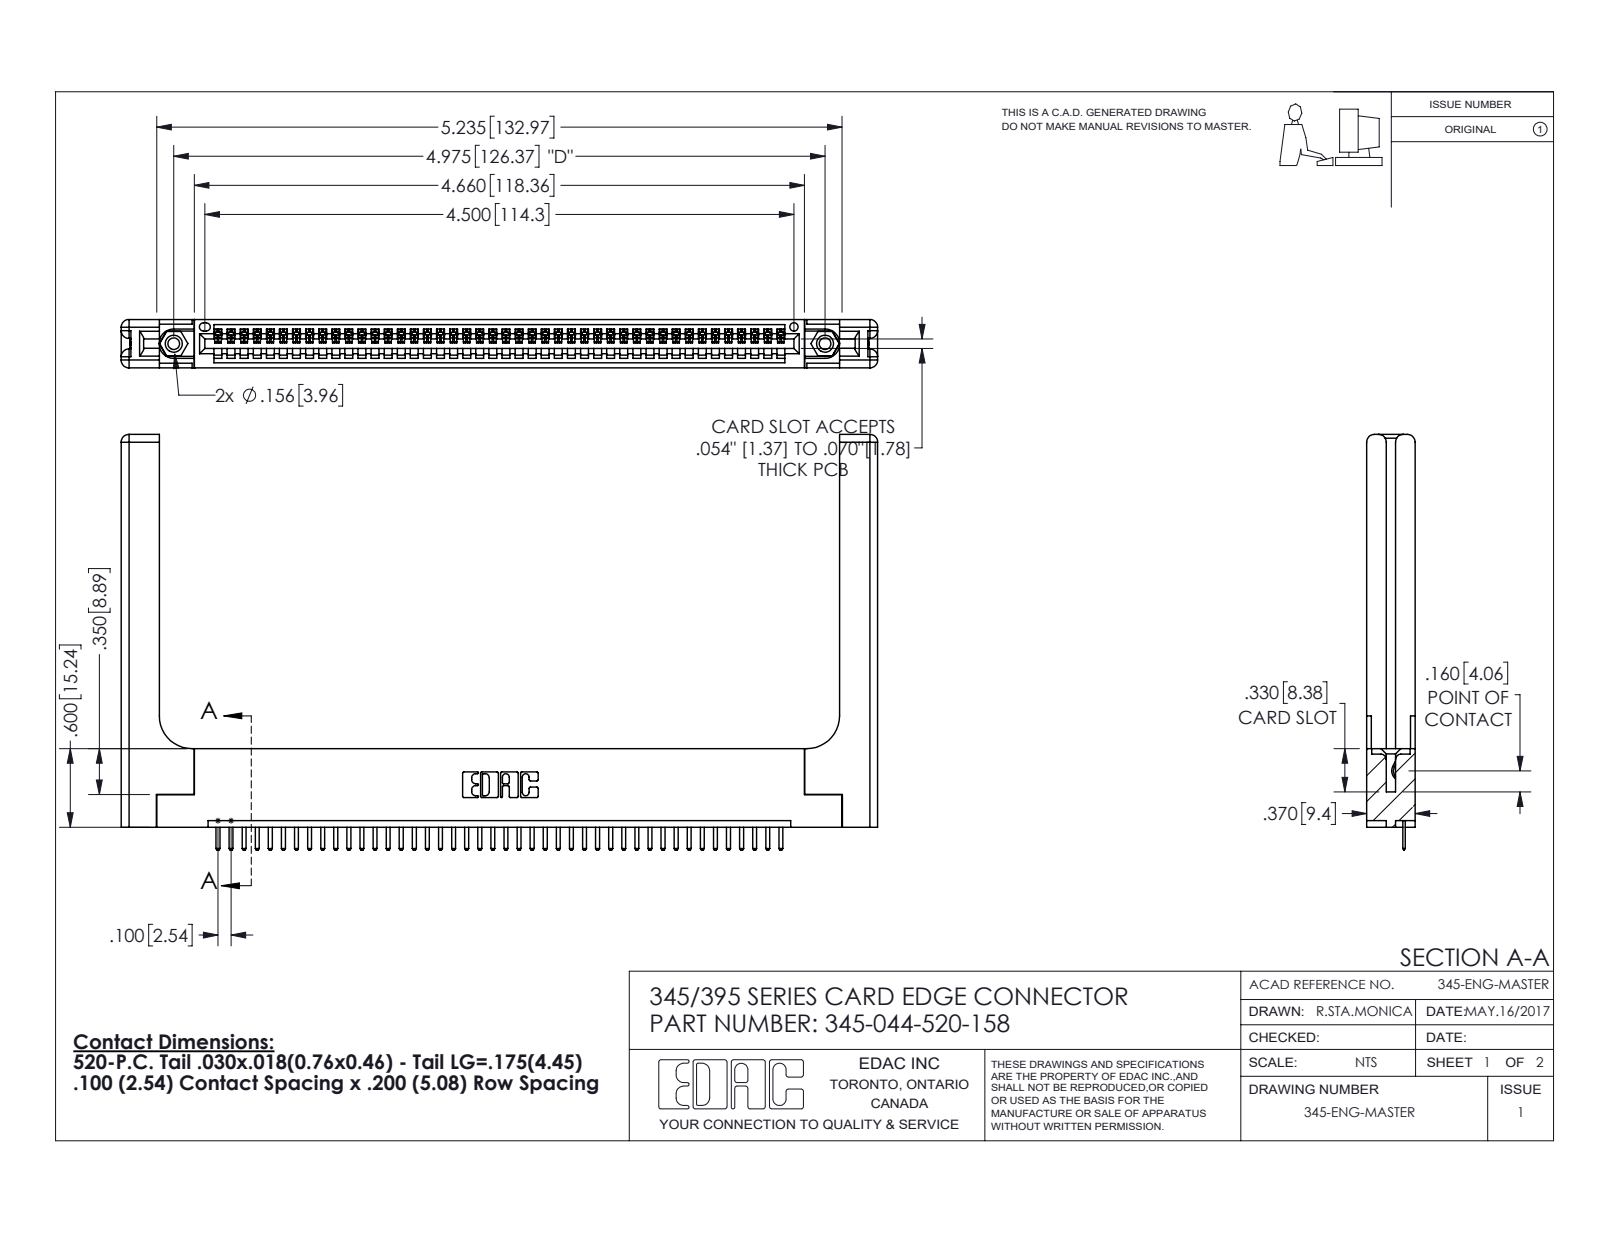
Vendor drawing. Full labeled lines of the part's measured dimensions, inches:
Part name (STEP PRODUCT): 345-250-001_345-250-001-102; 345-044-520-158; 345-220-058_345-220-058; 345-292-001_345-293-120 (+1 more)
STEP written by: SolidWorks 2016 (CONFIG_CONTROL_DESIGN)
Units: inches
Bodies: 49 solids, 3110 faces (2076 planar, 974 cylindrical, 60 other)
Overall size (bounding box): 5.779 × 3.175 × 0.37
Volume: 1.363 in³ · Surface area: 36.11 in²
Round holes (diameter × count): ⌀0.089 ×2, ⌀0.125 ×2, ⌀0.156 ×2, ⌀0.064 ×1
Round bosses / shafts (diameter × count): ⌀0.155 ×2
Partial cylindrical surfaces — rounded edges, fillets, slot ends (radius × count): R0.01 ×90, R0.006 ×88, R0.01 ×22, R0.06 ×16, R0.007 ×6, R0.031 ×6, R0.026 ×3, R0.03 ×2
Main face-to-face distances: 0.37, 0.072, 0.298, 0.2, 0.098, 0.272, 0.025, 0.148, 0.15, 0.225
Hole centre spacings: 0.27, 4.739, 4.975
